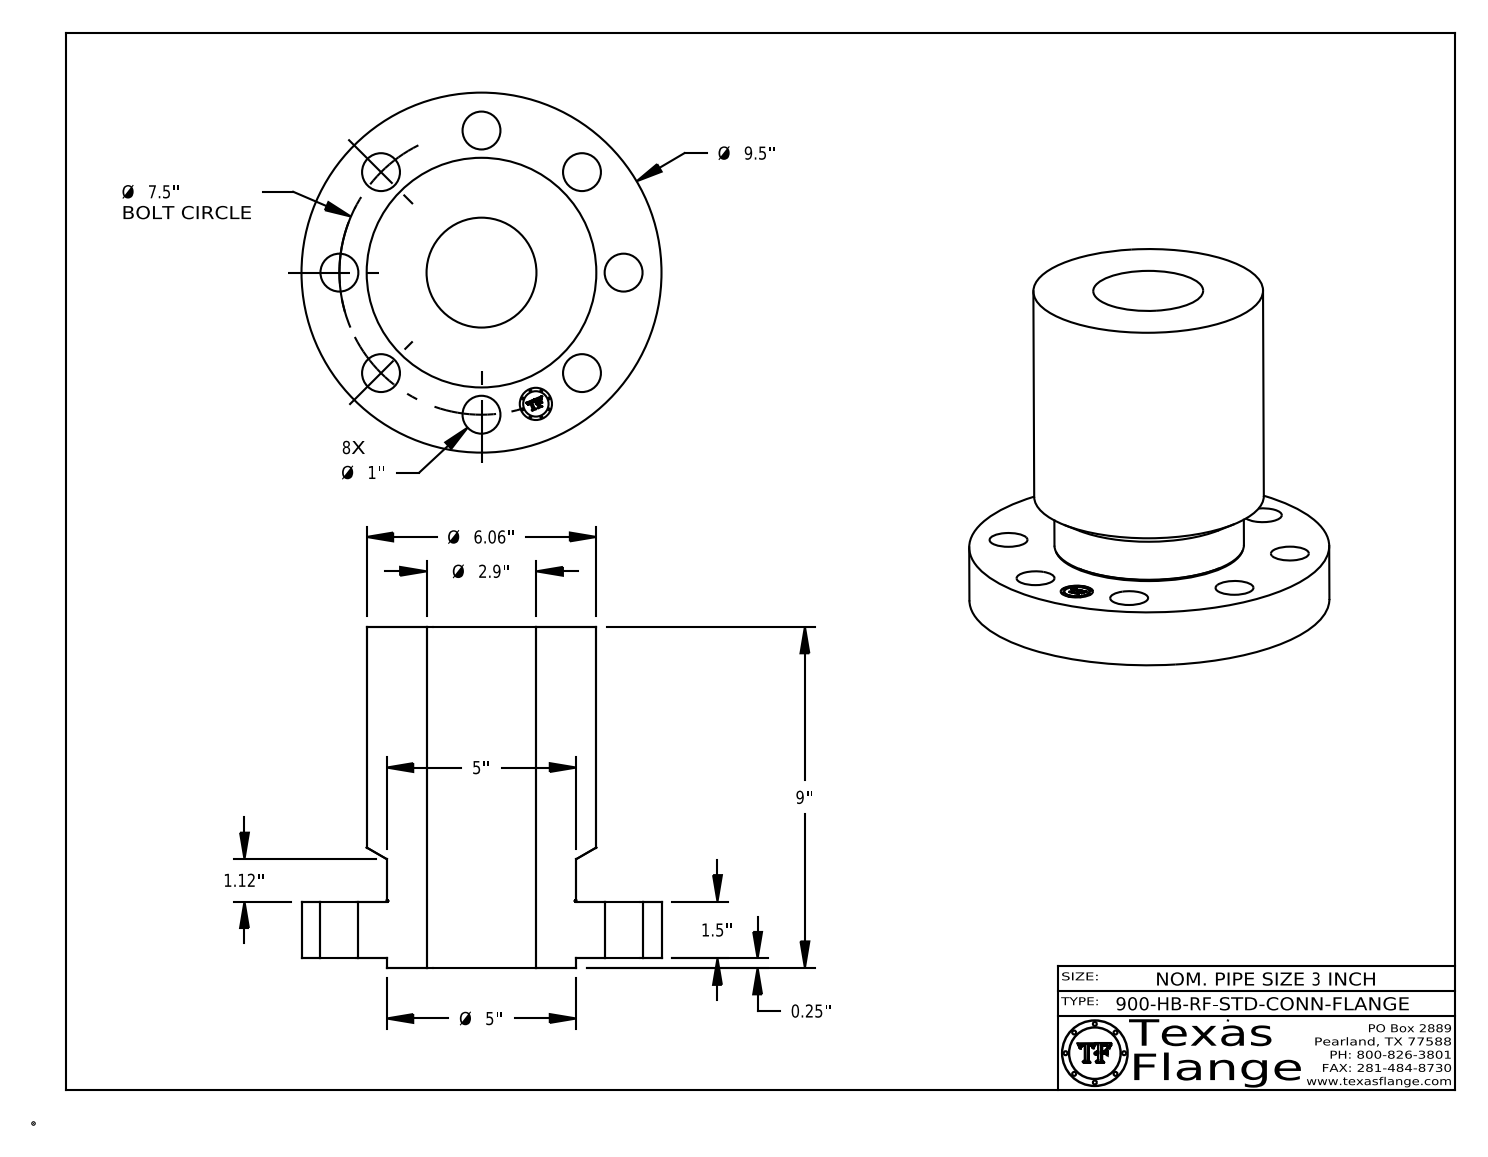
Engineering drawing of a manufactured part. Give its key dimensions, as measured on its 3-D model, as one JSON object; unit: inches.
{"part_name": "3-900-HB-RF-STD-CONN-FLANGE", "step_written_by": "CATIA V5 STEP AP214 (AUTOMOTIVE_DESIGN)", "units": "inches", "bodies": {"solids": 1, "faces": 421, "planar": 369, "cylindrical": 46, "other": 6}, "overall_size": [9.5, 9.5, 9], "volume_in3": 239.7, "surface_area_in2": 433.3, "round_holes": [[1, 8], [0.85, 1], [2.9, 1]], "round_bosses_or_shafts": [[0.051, 8], [9.5, 1], [6.06, 1], [5, 1], [0.67, 1]], "face_to_face_distances": [1.5, 8.75, 7.25, 0.25, 1.75, 9, 1.745, 1.495, 7.255, 0.254], "hole_center_spacings": [3.75, 2.87, 5.303, 6.929, 1.463, 6.236, 7.356, 7.5]}
